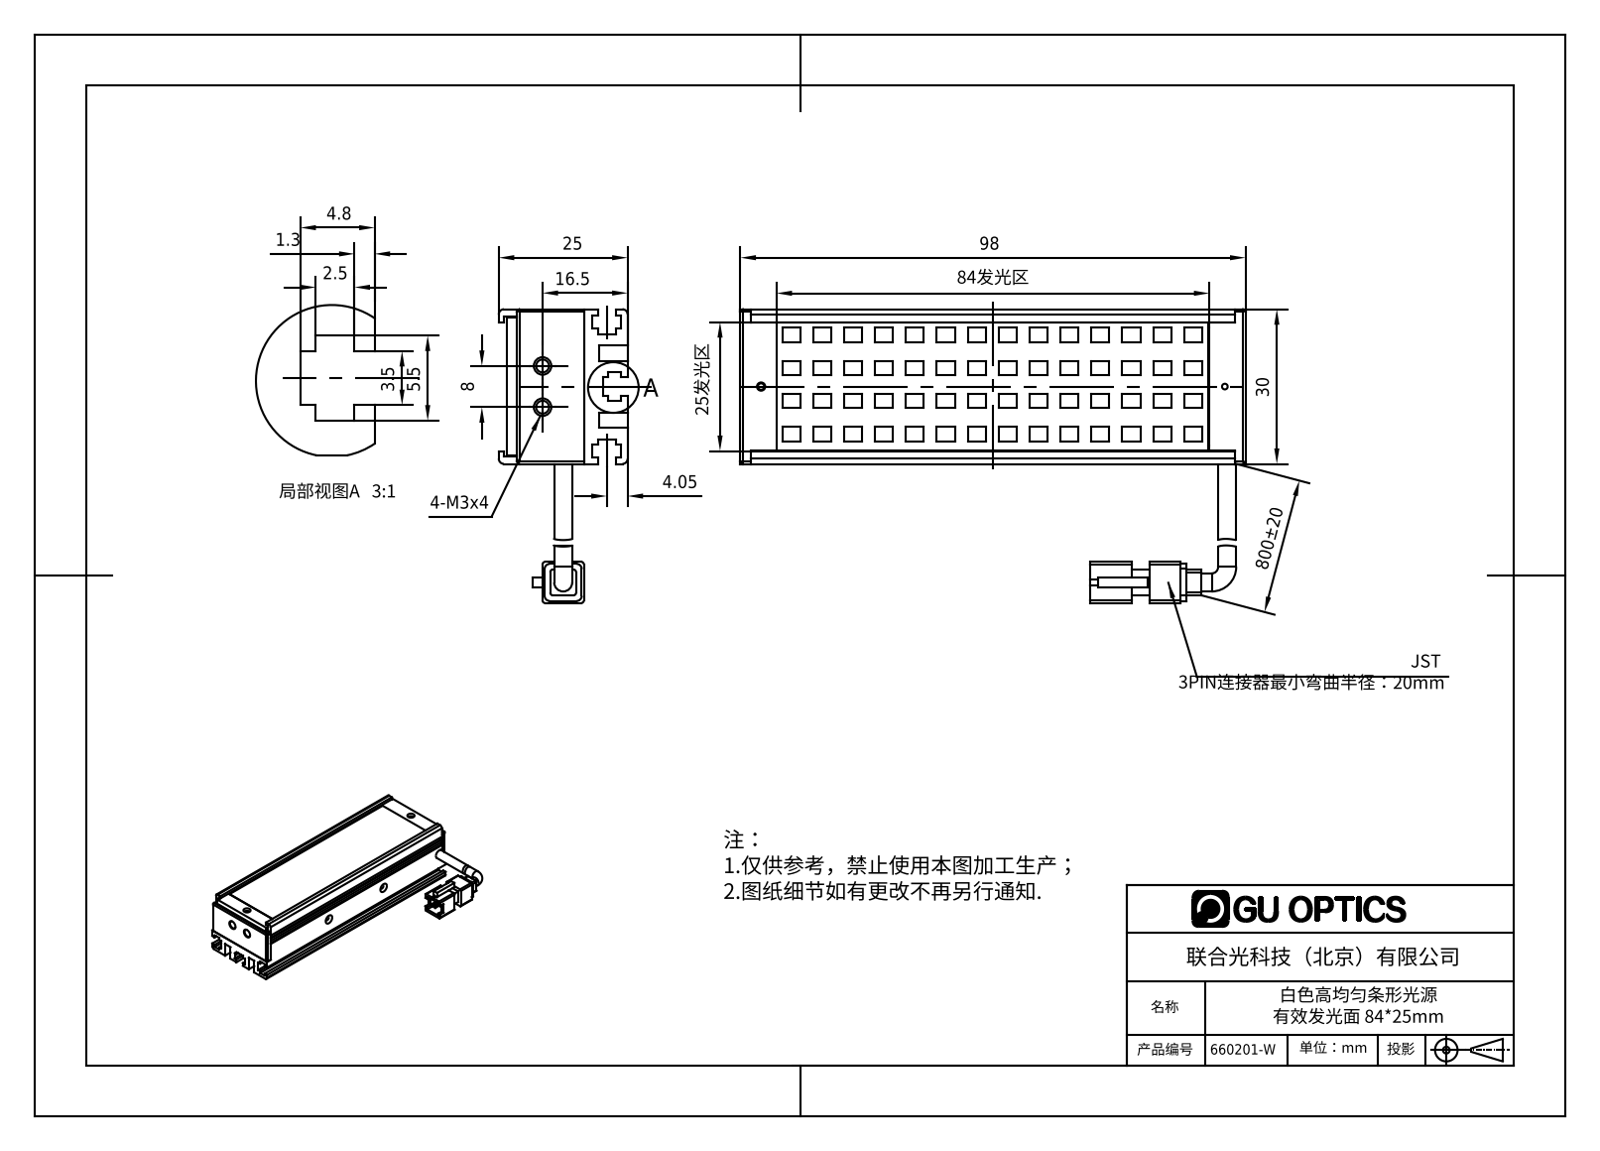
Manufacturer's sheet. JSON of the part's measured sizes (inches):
{"part_name": "660201-W", "step_written_by": "SolidWorks 2016 (AUTOMOTIVE_DESIGN)", "units": "inches", "bodies": {"solids": 6, "faces": 724, "planar": 538, "cylindrical": 83, "other": 103}, "overall_size": [3.858, 2.244, 0.984], "volume_in3": 2.211, "surface_area_in2": 56.43, "round_holes": [[0.063, 5], [0.059, 2], [0.067, 2], [0.098, 2], [0.11, 2], [0.118, 2], [0.043, 1], [0.049, 1], [0.079, 1]], "round_bosses_or_shafts": [[0.138, 2]], "partial_cylinders_radius": [[0.039, 12], [0.02, 8], [0.065, 1]], "face_to_face_distances": [0.039, 0.512, 0.079, 0.098, 0.118, 0.374, 0.083, 0.177, 1.083, 0.335], "hole_center_spacings": [1.181, 3.543, 0.276, 1.209, 2.362, 2.376, 3.554, 0.315]}
